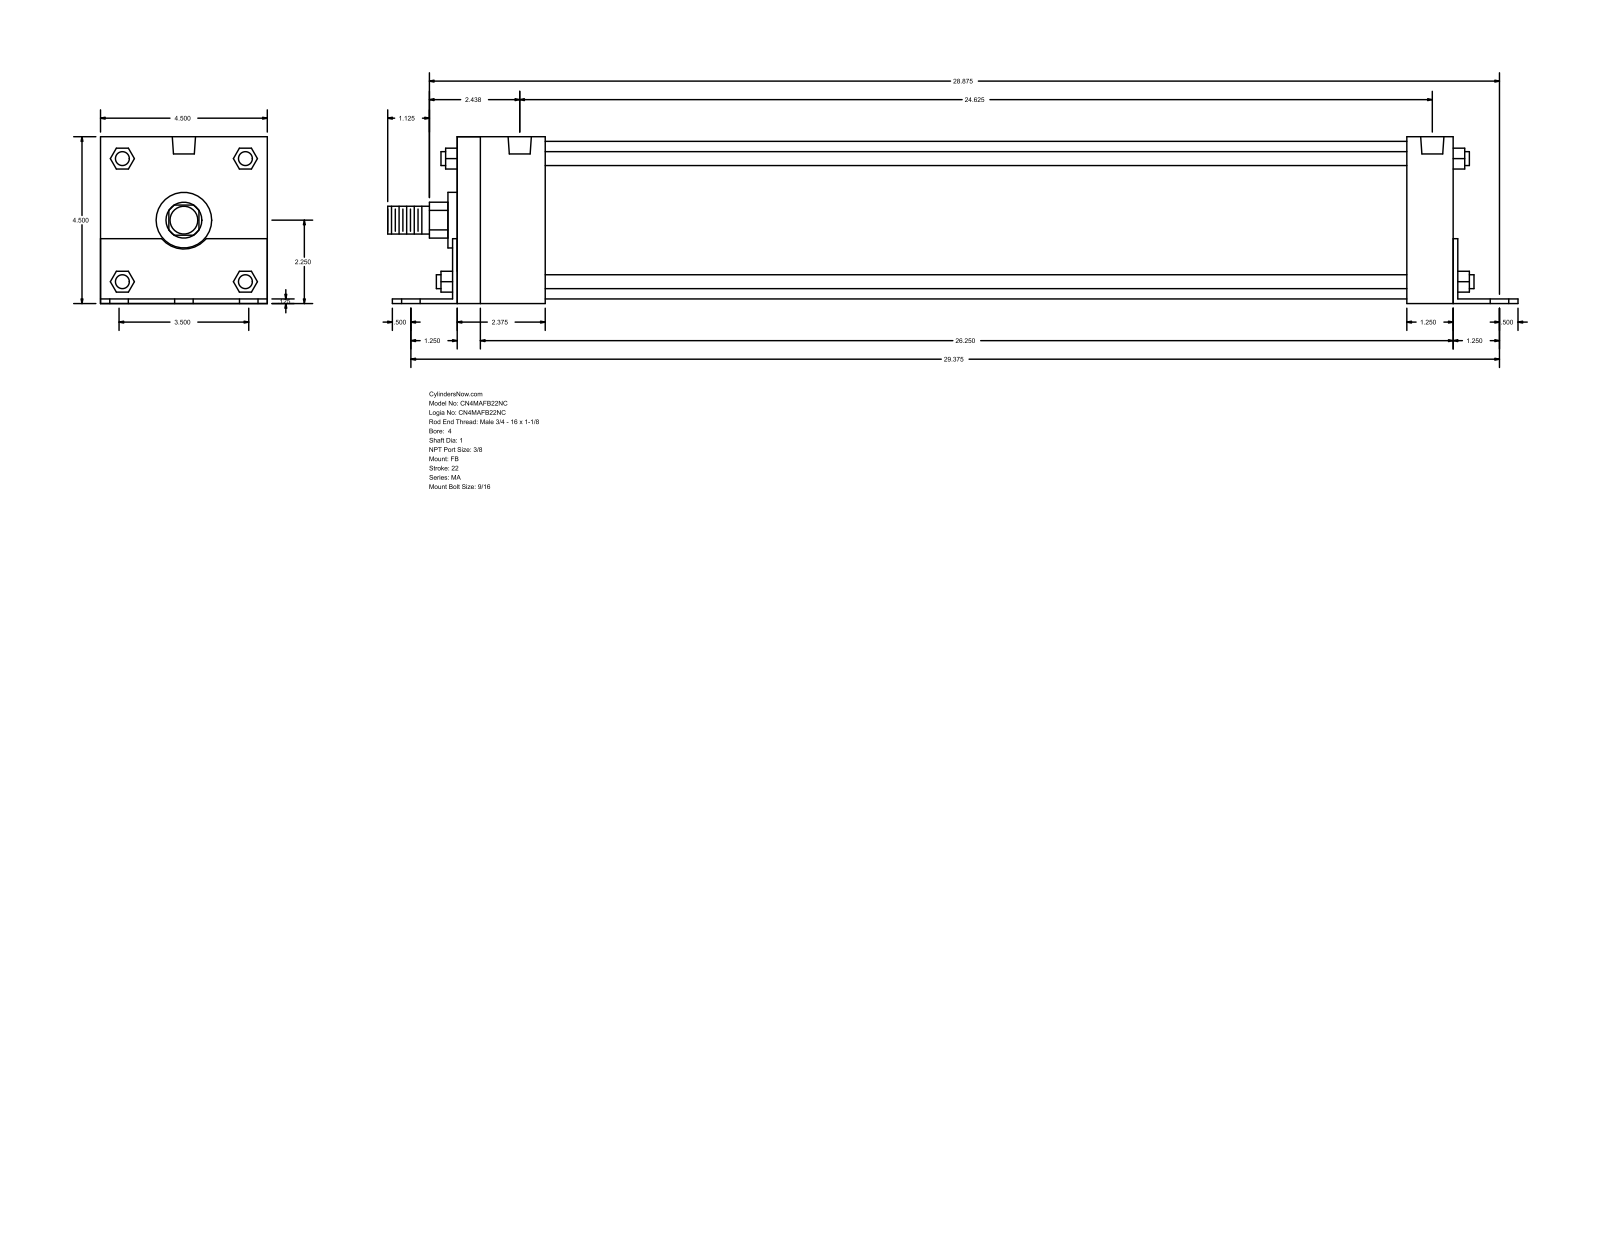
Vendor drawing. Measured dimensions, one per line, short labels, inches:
name: MA_FB__0400_1
written by: GSSL Pune (CONFIG_CONTROL_DESIGN)
unit: in
bodies: 0 solids, 140 faces (105 planar, 35 cylindrical, 0 other)
size: 30.5 × 4.502 × 4.5
holes: 6× ⌀0.563, 4× ⌀0.437, 2× ⌀0.627
bosses: 4× ⌀0.375, 1× ⌀4.25, 1× ⌀1.5, 1× ⌀1, 1× ⌀0.75
rounds: 1× R0.484, 1× R0.78
face distances: 4.5, 0.125, 4.502, 0.123, 4.377, 26.875, 0.125, 27.125, 27, 27
hole spacings: 1.75, 29.427, 29.375, 2.519, 2.657, 3.419, 3.5, 3.581
